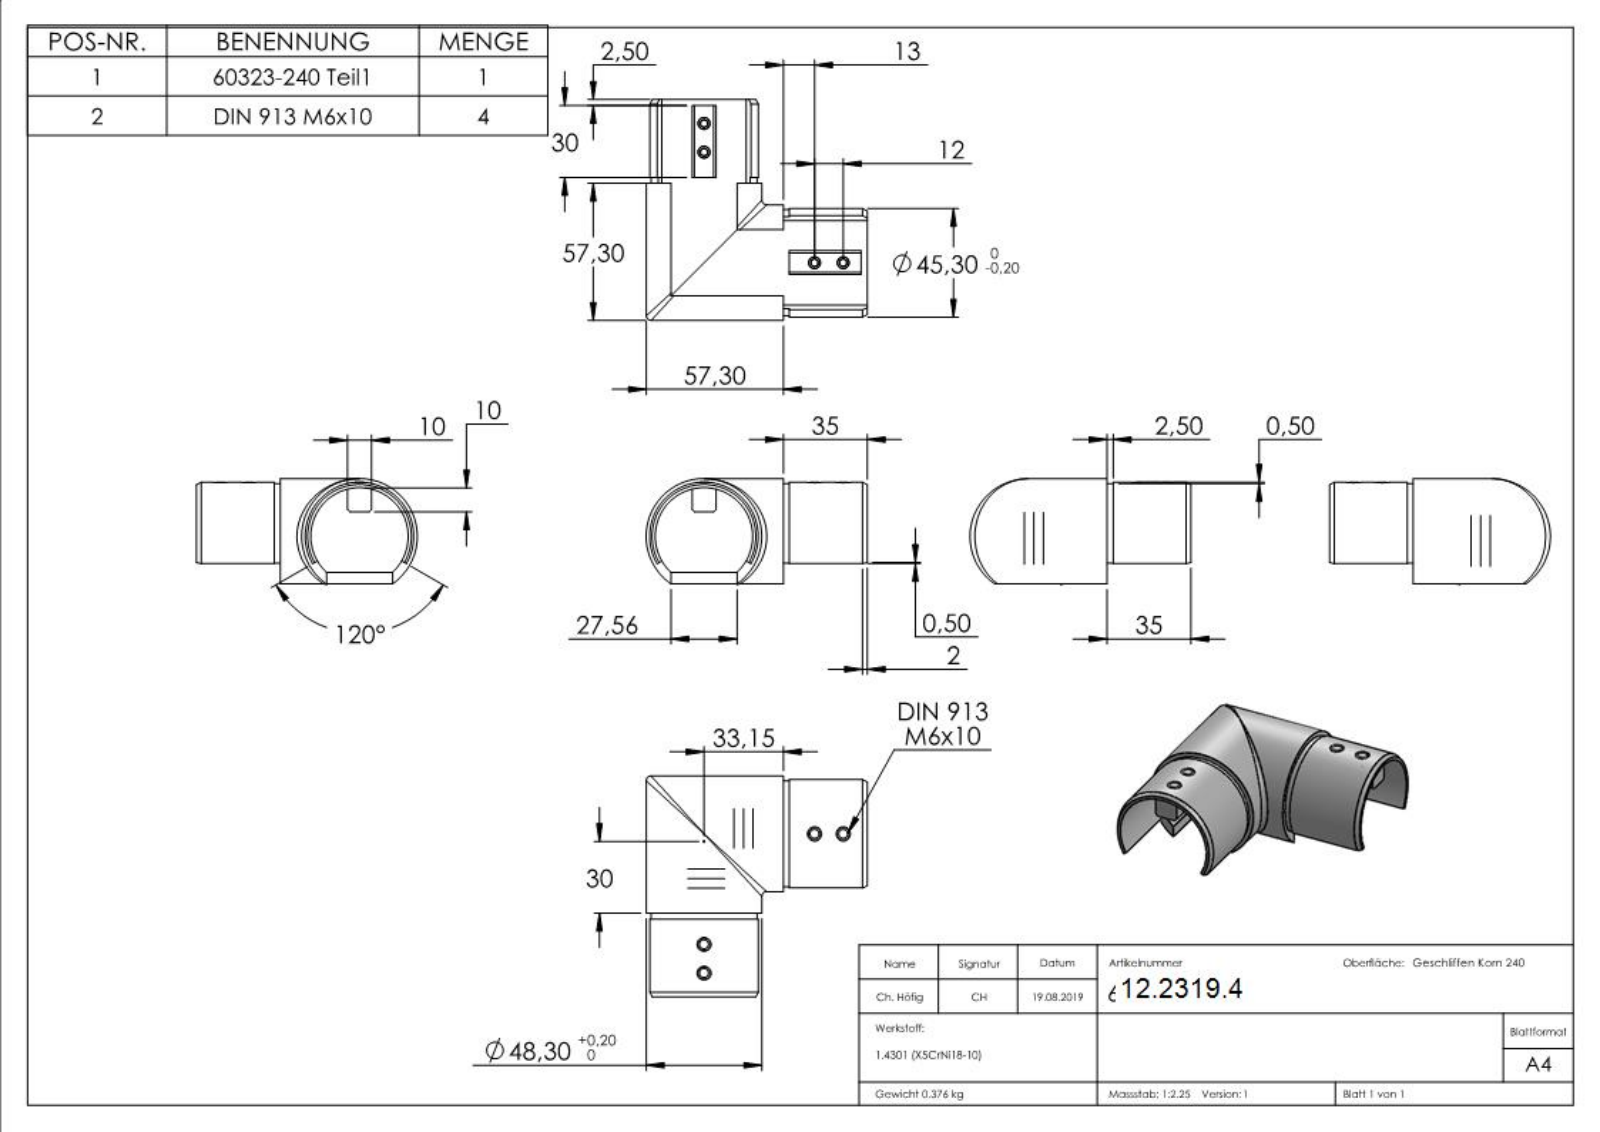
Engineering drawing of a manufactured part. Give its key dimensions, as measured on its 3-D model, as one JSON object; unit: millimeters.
{"part_name": "60323-240; 6032X-240 Teil1 Konfig Verlaufecke Nutrohr_60323-240 Teil1; DIN913_DIN 913 M6x10", "step_written_by": "SolidWorks 2015 (CONFIG_CONTROL_DESIGN)", "units": "millimeters", "bodies": {"solids": 5, "faces": 395, "planar": 200, "cylindrical": 40, "other": 155}, "overall_size": [92.3, 92.3, 44.18], "volume_mm3": 47607, "surface_area_mm2": 32048, "round_holes": [[5, 4]], "round_bosses_or_shafts": [[6, 4], [48.3, 2]], "partial_cylinders_radius": [[20.35, 2], [22.15, 2], [22.65, 2]], "face_to_face_distances": [8.78, 18.78, 10, 38.15, 28.15, 2.5, 46.93, 32.5, 49.43, 40.65], "hole_center_spacings": [12, 74.24, 65.27, 82.24]}
